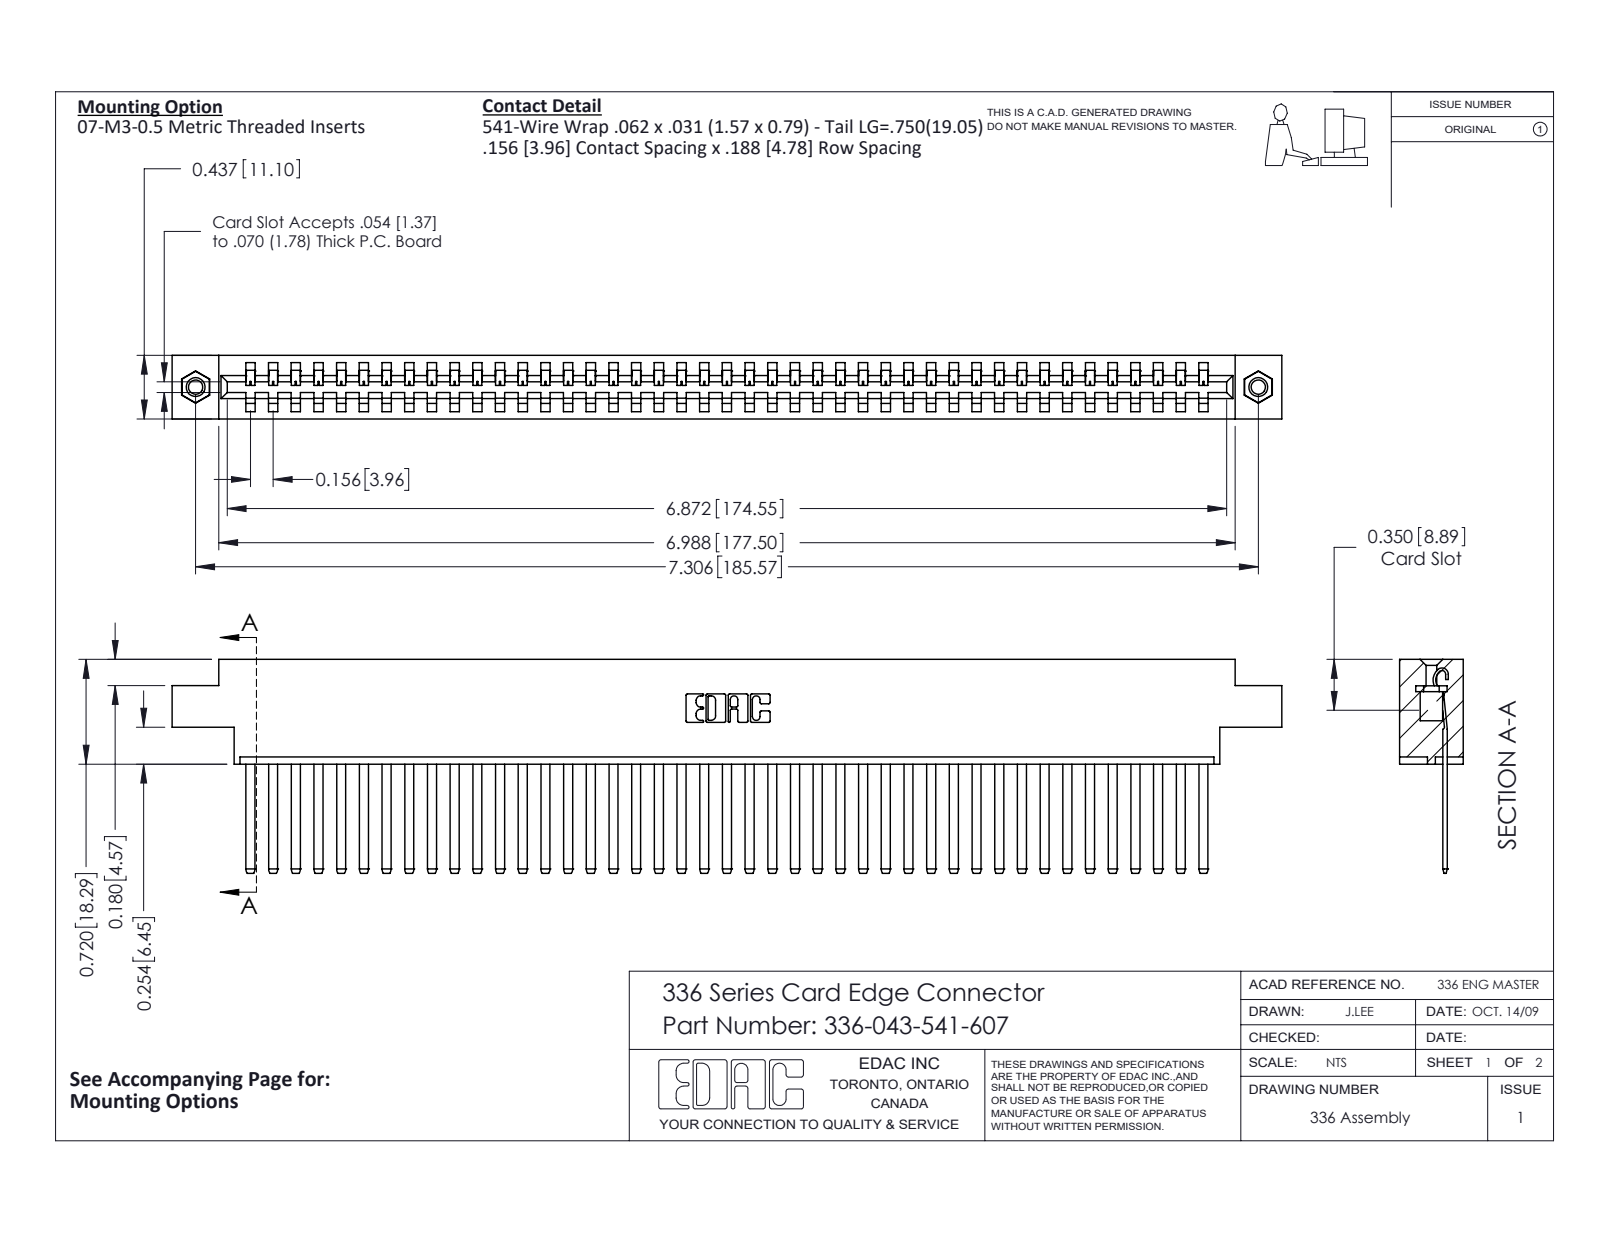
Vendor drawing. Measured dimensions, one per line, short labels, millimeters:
name: 345-250-001_345-250-005-103; 336-043-541-607; 336 Part_Offset - .156 Dia - TI; 336-290-001_336-290-541
written by: SolidWorks 2020 (CONFIG_CONTROL_DESIGN)
unit: mm
bodies: 46 solids, 2328 faces (1568 planar, 744 cylindrical, 16 other)
size: 193.8 × 37.3 × 11.1
volume: 28 250 mm³; area: 30 880 mm²
holes: 2× ⌀2.5, 2× ⌀3.2, 2× ⌀4
bosses: 2× ⌀3.9
rounds: 86× R0.1, 86× R1.4, 22× R0.3, 6× R0.2, 6× R0.8, 3× R0.7, 2× R0.6, 2× R1
face distances: 11.1, 4.6, 8.3, 3.6, 7.5, 2.8, 0.8, 6.5, 1.3, 3.3
hole spacings: 185.6
